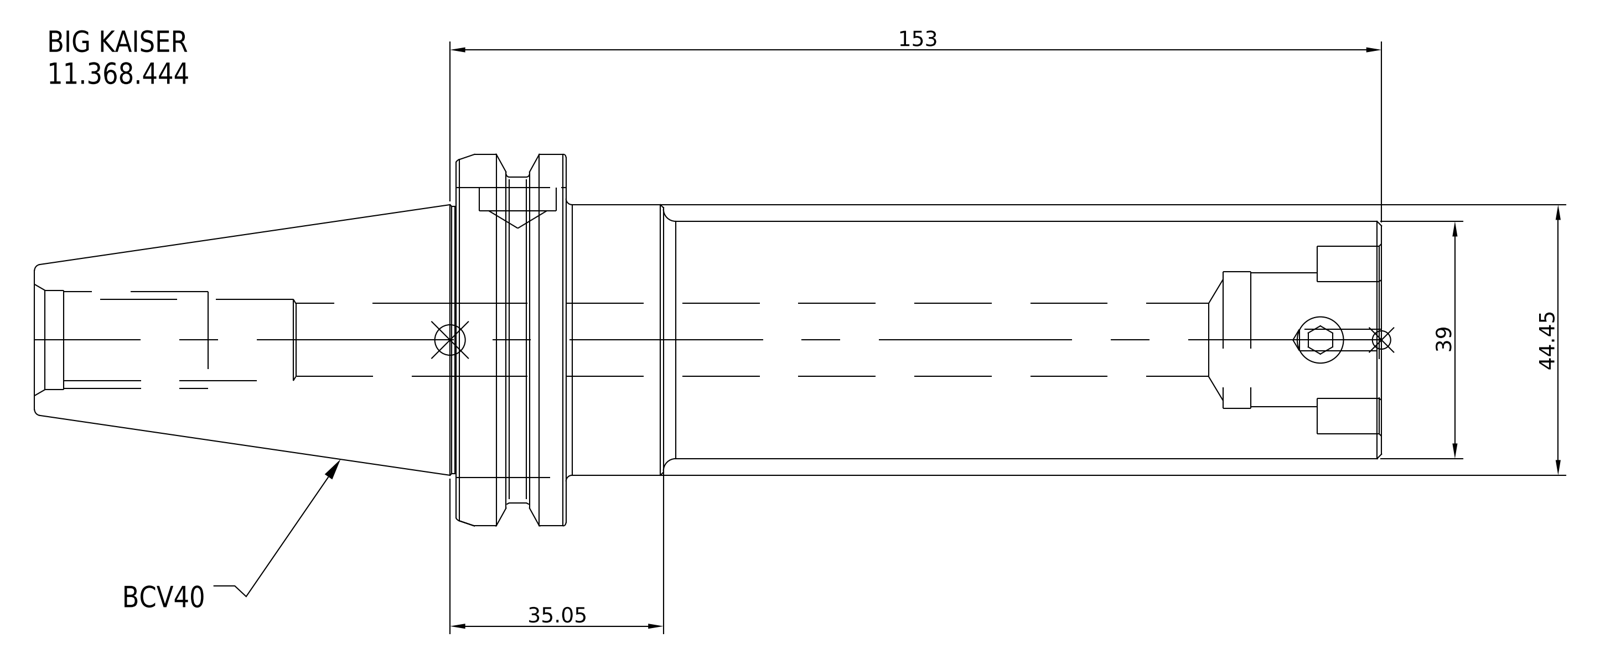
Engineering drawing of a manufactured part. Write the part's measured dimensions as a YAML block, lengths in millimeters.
part_name: "11.368.444"
step_written_by: "SolidWorks 2021 (CONFIG_CONTROL_DESIGN)"
units: millimeters
bodies: {solids: 1, faces: 16, planar: 7, cylindrical: 6, other: 3}
overall_size: [221.25, 63.5, 63.5]
volume: 283046
surface_area: 33809
round_bosses_or_shafts:
  - {diameter: 63.5, count: 1}
  - {diameter: 56.36, count: 1}
  - {diameter: 44.45, count: 1}
  - {diameter: 39, count: 1}
face_to_face_distances: [15.88, 133.95, 149.83, 221.25, 87.3, 71.42, 117.95, 16, 31.88, 103.3]
